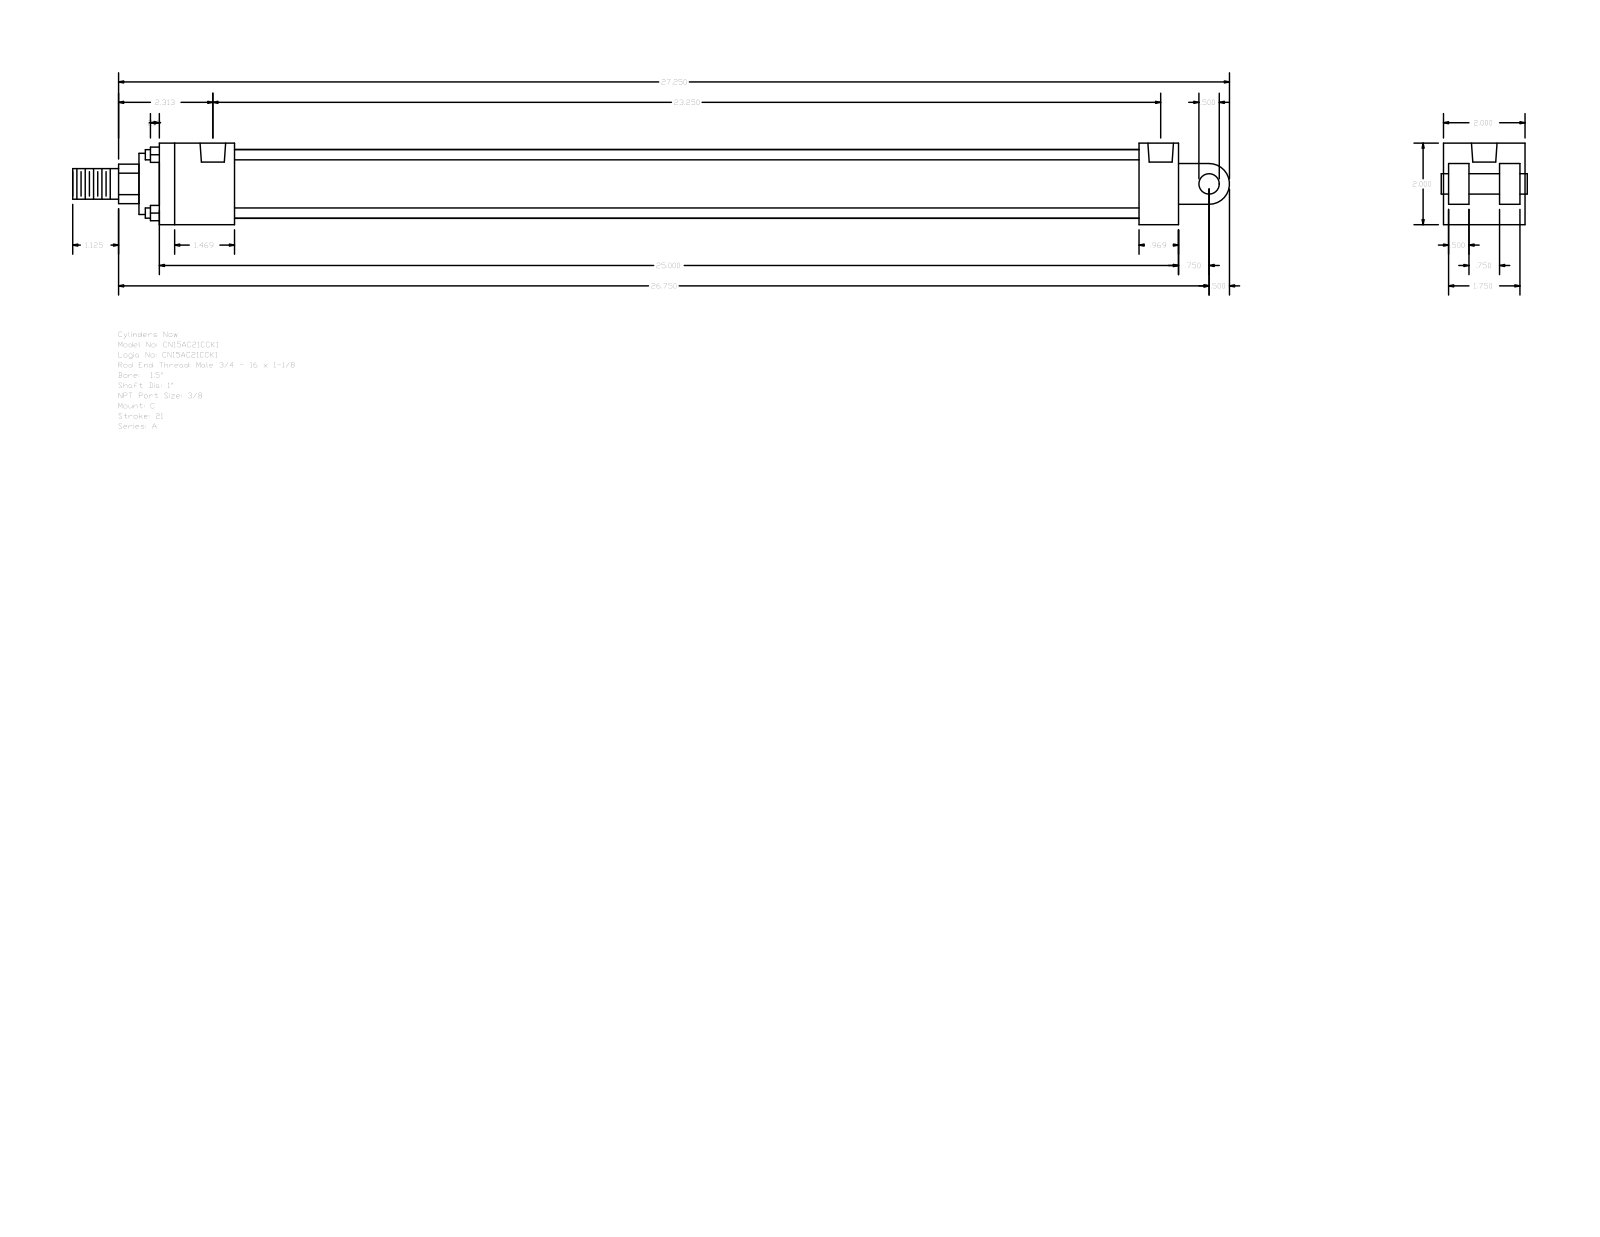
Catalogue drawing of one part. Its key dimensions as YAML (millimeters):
part_name: "A_C__0150_1"
step_written_by: "GSSL Pune (CONFIG_CONTROL_DESIGN)"
units: millimeters
bodies: {solids: 0, faces: 99, planar: 70, cylindrical: 29, other: 0}
overall_size: [720.73, 50.8, 50.8]
round_holes:
  - {diameter: 5.56, count: 4}
  - {diameter: 15.93, count: 2}
round_bosses_or_shafts:
  - {diameter: 6.35, count: 4}
  - {diameter: 42.93, count: 1}
  - {diameter: 38.1, count: 1}
  - {diameter: 25.4, count: 1}
  - {diameter: 19.05, count: 1}
  - {diameter: 12.7, count: 1}
partial_cylinders:
  - {radius: 12.29, count: 1}
  - {radius: 12.7, count: 1}
face_to_face_distances: [50.8, 12.7, 3.17, 15.87, 47.63, 34.93, 31.76, 635, 38.1, 610.39]
hole_center_spacings: [3.97, 582.61, 586.58, 590.55]
